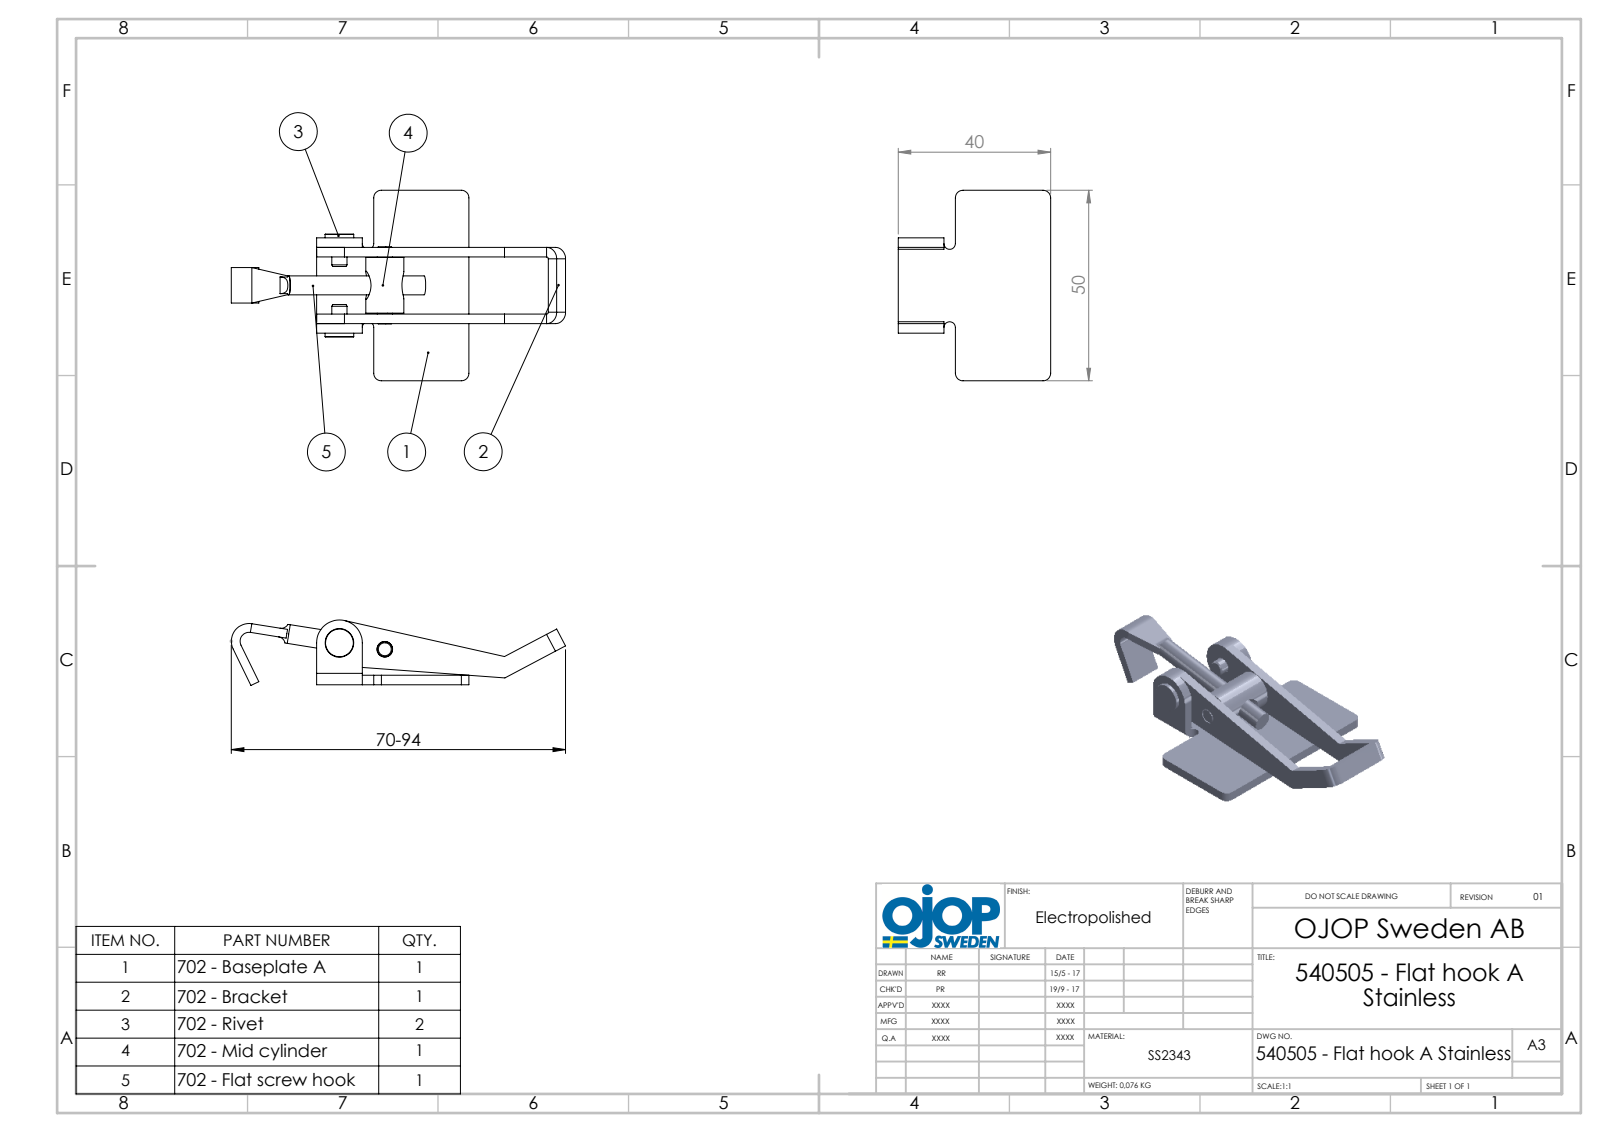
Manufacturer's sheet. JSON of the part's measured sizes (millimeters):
{"part_name": "540505 - Flat hook A Stainless; 702 - Rulle; 702 - Ansatsnit; 702 - A (+2 more)", "step_written_by": "SolidWorks 2015 (AUTOMOTIVE_DESIGN)", "units": "millimeters", "bodies": {"solids": 6, "faces": 144, "planar": 69, "cylindrical": 59, "other": 16}, "overall_size": [87.75, 50, 17.18], "volume_mm3": 9960, "surface_area_mm2": 9857, "round_holes": [[4.1, 2], [5, 2]], "round_bosses_or_shafts": [[4, 2], [10, 1], [7.5, 1], [6, 1], [4.96, 1], [4.95, 1]], "partial_cylinders_radius": [[2, 6], [0.5, 4], [3, 4], [1.5, 2], [2.35, 1], [4.65, 1], [6, 1]], "face_to_face_distances": [2.5, 17.5, 20, 15, 5, 22.5, 25, 2.65, 2.3, 12.5], "hole_center_spacings": [12.03]}
